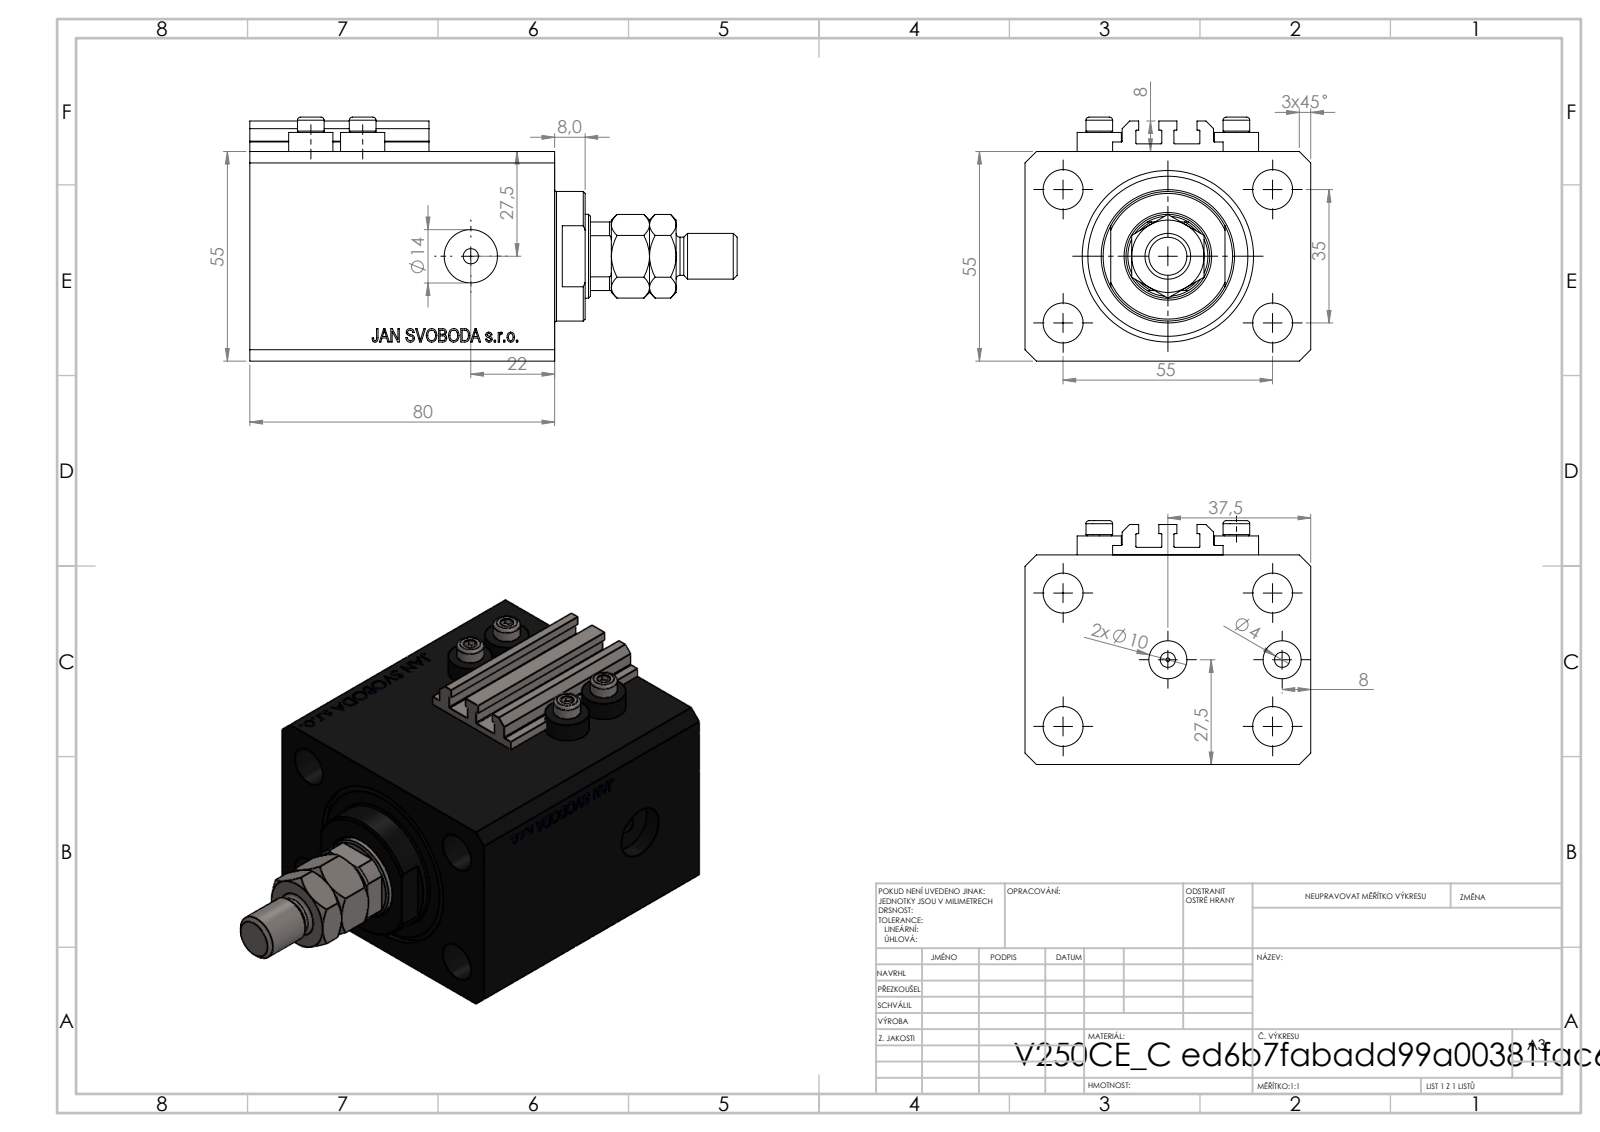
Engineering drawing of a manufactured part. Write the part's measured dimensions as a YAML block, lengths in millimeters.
part_name: "ALLEN BOLT V250CE; V250CE_C_VCP; V250CE_VC_C; MTA (+1 more)"
step_written_by: "SolidWorks 2019 (CONFIG_CONTROL_DESIGN)"
units: millimeters
bodies: {solids: 9, faces: 1091, planar: 519, cylindrical: 96, other: 476}
overall_size: [128, 75, 64]
volume: 311583
surface_area: 74200
round_holes:
  - {diameter: 4, count: 8}
  - {diameter: 10.5, count: 5}
  - {diameter: 10, count: 2}
  - {diameter: 14, count: 2}
  - {diameter: 1.25, count: 1}
  - {diameter: 22, count: 1}
  - {diameter: 32, count: 1}
  - {diameter: 45, count: 1}
round_bosses_or_shafts:
  - {diameter: 11.6, count: 4}
  - {diameter: 7, count: 4}
  - {diameter: 34, count: 1}
  - {diameter: 12, count: 1}
partial_cylinders:
  - {radius: 0.2, count: 10}
  - {radius: 10.5, count: 1}
face_to_face_distances: [55, 75, 80, 15, 65, 9.9, 55.1, 70.1, 3, 2.5]
hole_center_spacings: [32.6, 36, 13.6, 17.68, 35, 38.48, 55, 60.1]
